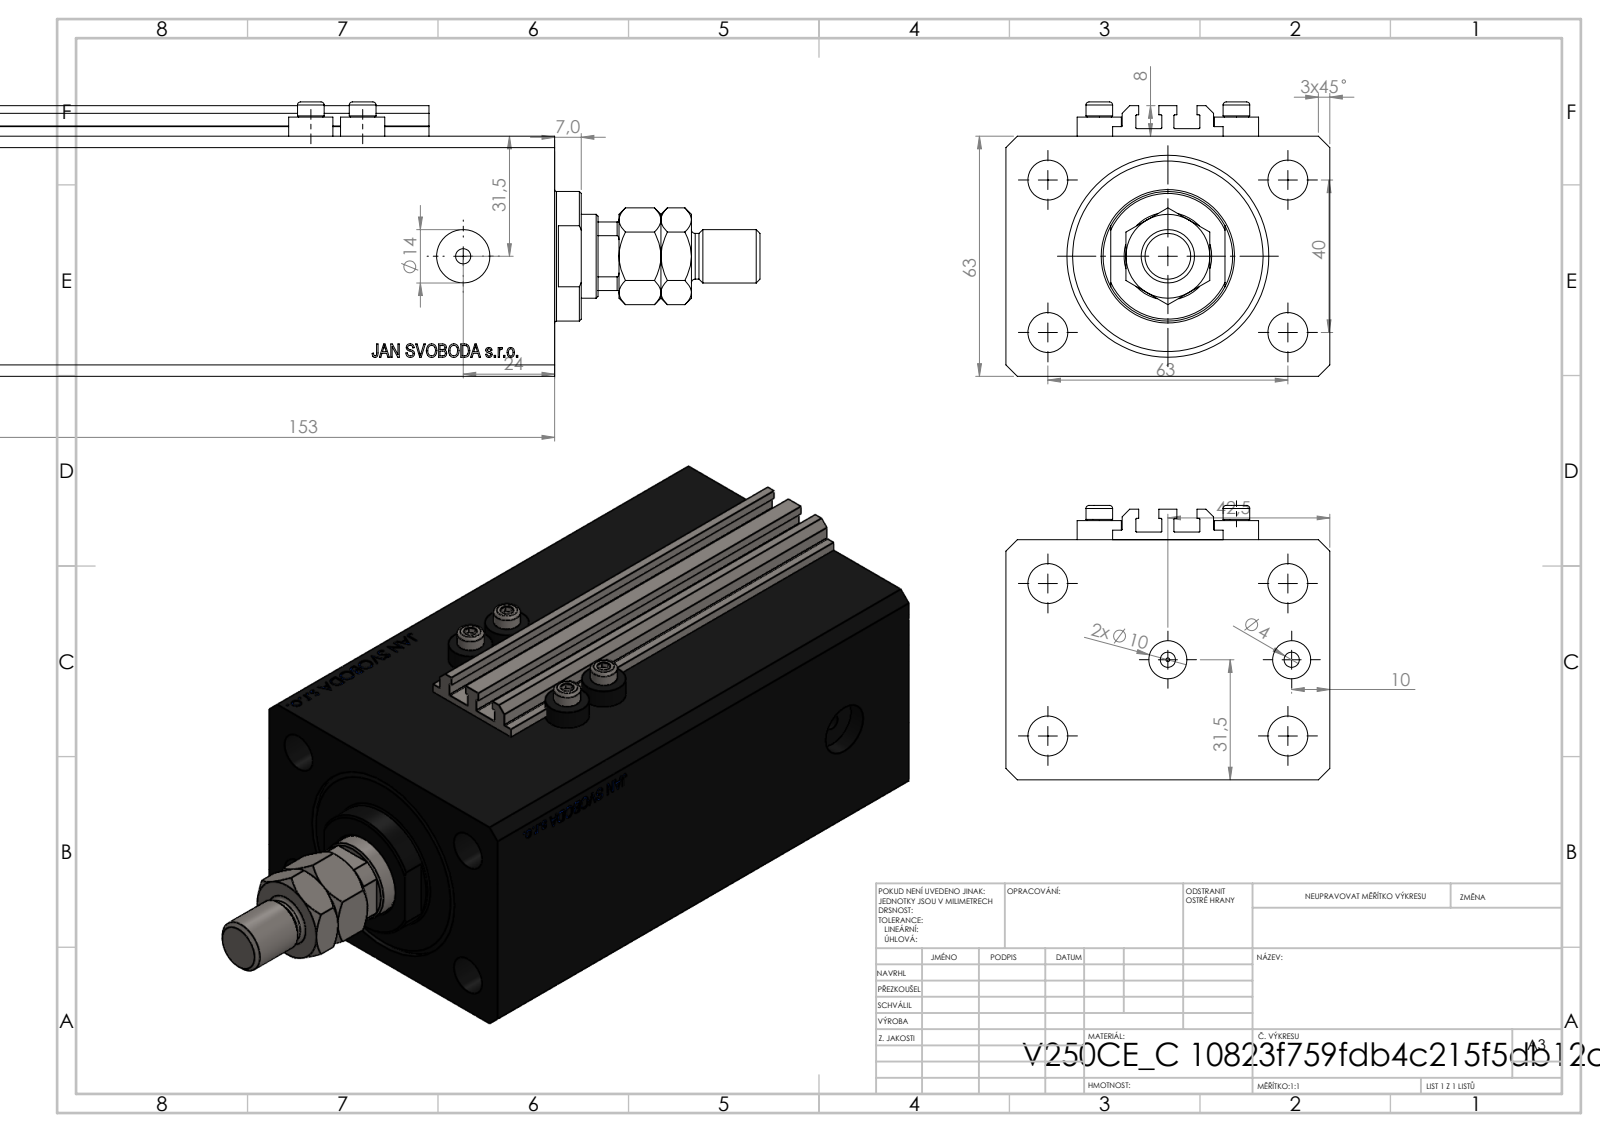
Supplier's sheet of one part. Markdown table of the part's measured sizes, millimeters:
| quantity | value |
| --- | --- |
| part name | MTA; ALLEN BOLT V250CE; V250CE_C_Body; V250CE_VC_C (+1 more) |
| STEP written by | SolidWorks 2019 (CONFIG_CONTROL_DESIGN) |
| units | millimeters |
| bodies | 9 solids, 1087 faces (519 planar, 92 cylindrical, 476 other) |
| overall size | 206.9 × 85 × 72 |
| volume | 724 650 mm³ |
| surface area | 140 853 mm² |
| round holes (diameter × count) | 4 × 8, 10.5 × 4, 10 × 2, 14 × 2, 1.25 × 1, 12.5 × 1, 22 × 1, 40 × 1, 53 × 1 |
| round bosses / shafts (diameter × count) | 11.6 × 4, 7 × 4, 34 × 1, 14 × 1, 12 × 1 |
| partial cylindrical surfaces (radius × count) | 0.2 × 10, 10.5 × 1 |
| main face-to-face distances | 63, 85, 153, 125.9, 27.1, 11.4, 114.5, 141.6, 2.5, 2 |
| hole center spacings | 37.31, 13.6, 20.02, 36, 38.48, 40, 63, 67.05 |
